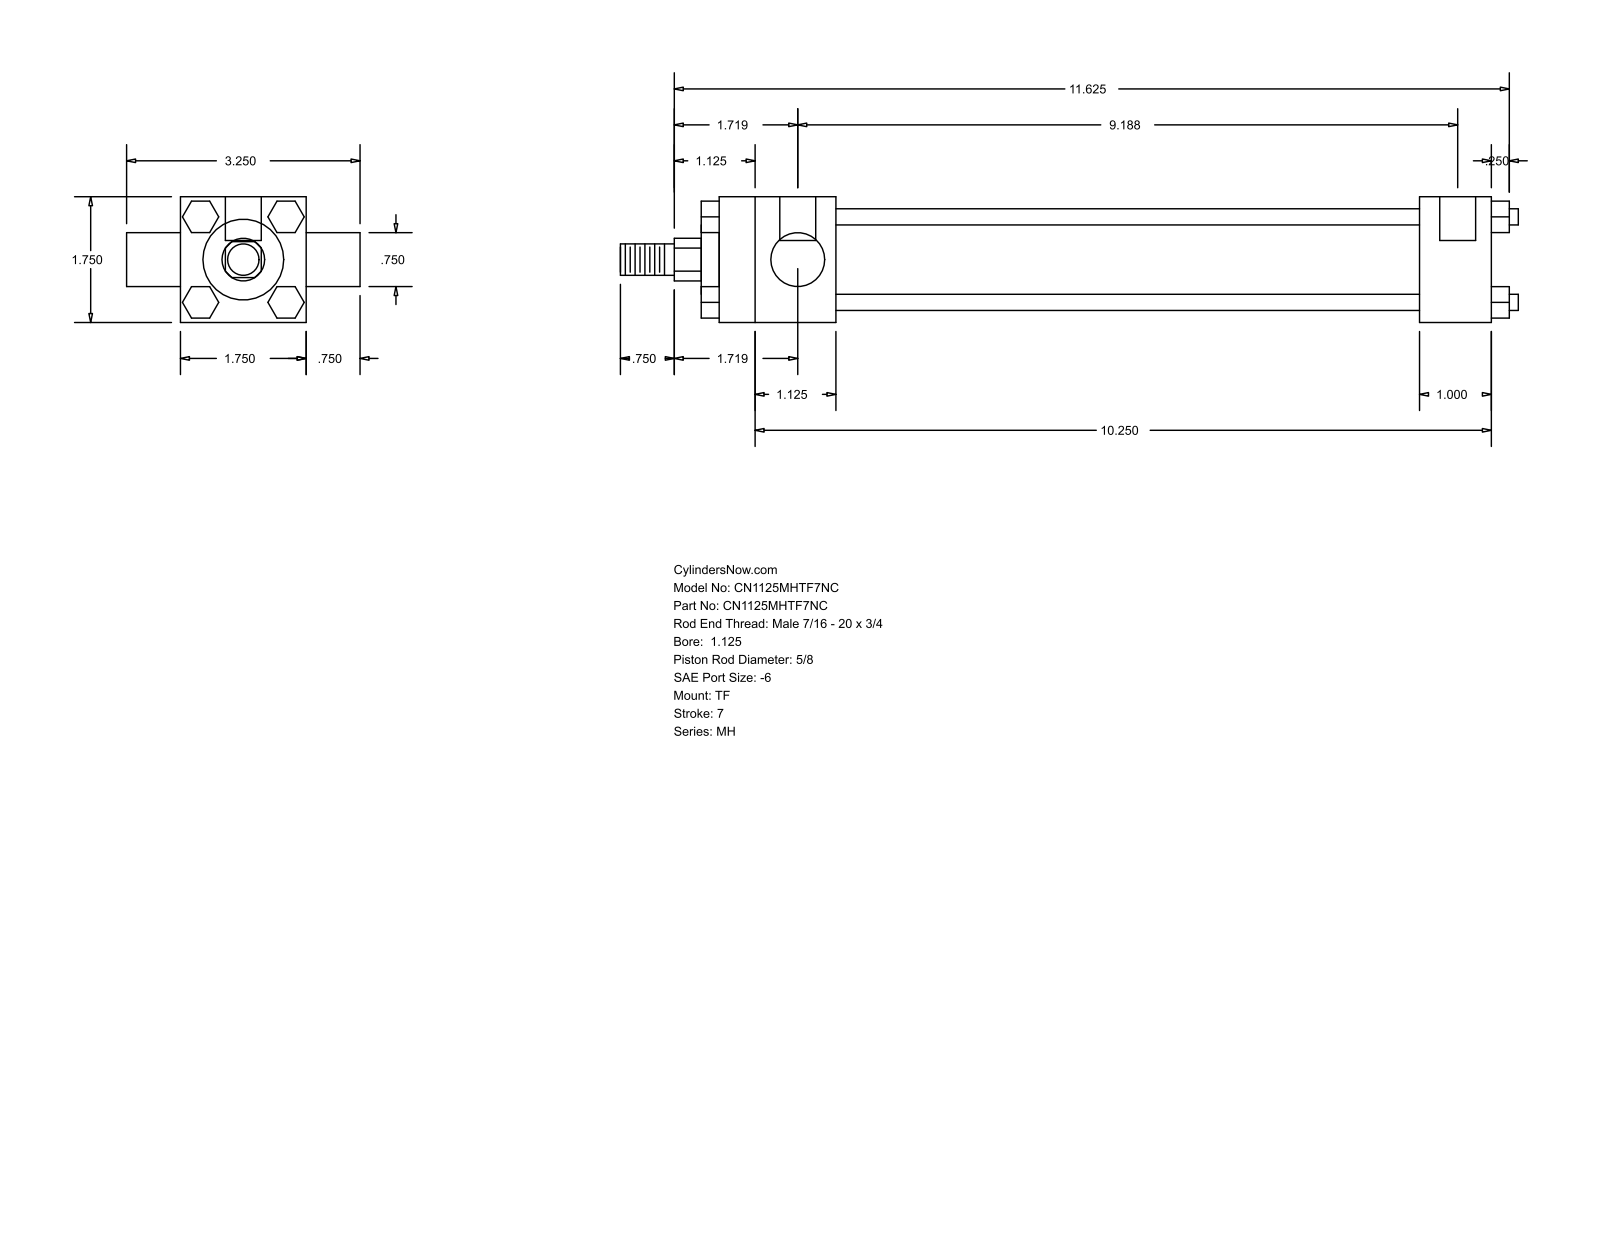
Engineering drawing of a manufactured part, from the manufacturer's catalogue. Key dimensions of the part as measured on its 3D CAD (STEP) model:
Part name (STEP PRODUCT): MH_TF__0112_0.625
STEP written by: GSSL Pune (CONFIG_CONTROL_DESIGN)
Units: millimetres
Bodies: 0 solids, 120 faces (92 planar, 28 cylindrical, 0 other)
Overall size (bounding box): 317.5 × 82.55 × 44.45
Round holes (diameter × count): ⌀5.56 ×3, ⌀12.7 ×2
Round bosses / shafts (diameter × count): ⌀5.71 ×4, ⌀34.92 ×1, ⌀28.57 ×1, ⌀19.05 ×1, ⌀15.88 ×1, ⌀11.11 ×1
Partial cylindrical surfaces — rounded edges, fillets, slot ends (radius × count): R7.54 ×1
Main face-to-face distances: 44.46, 11.11, 206.37, 231.78, 25.41, 41.27, 247.64, 273.05, 47.62, 6.35
Hole centre spacings: 3.17, 230.19, 233.36
